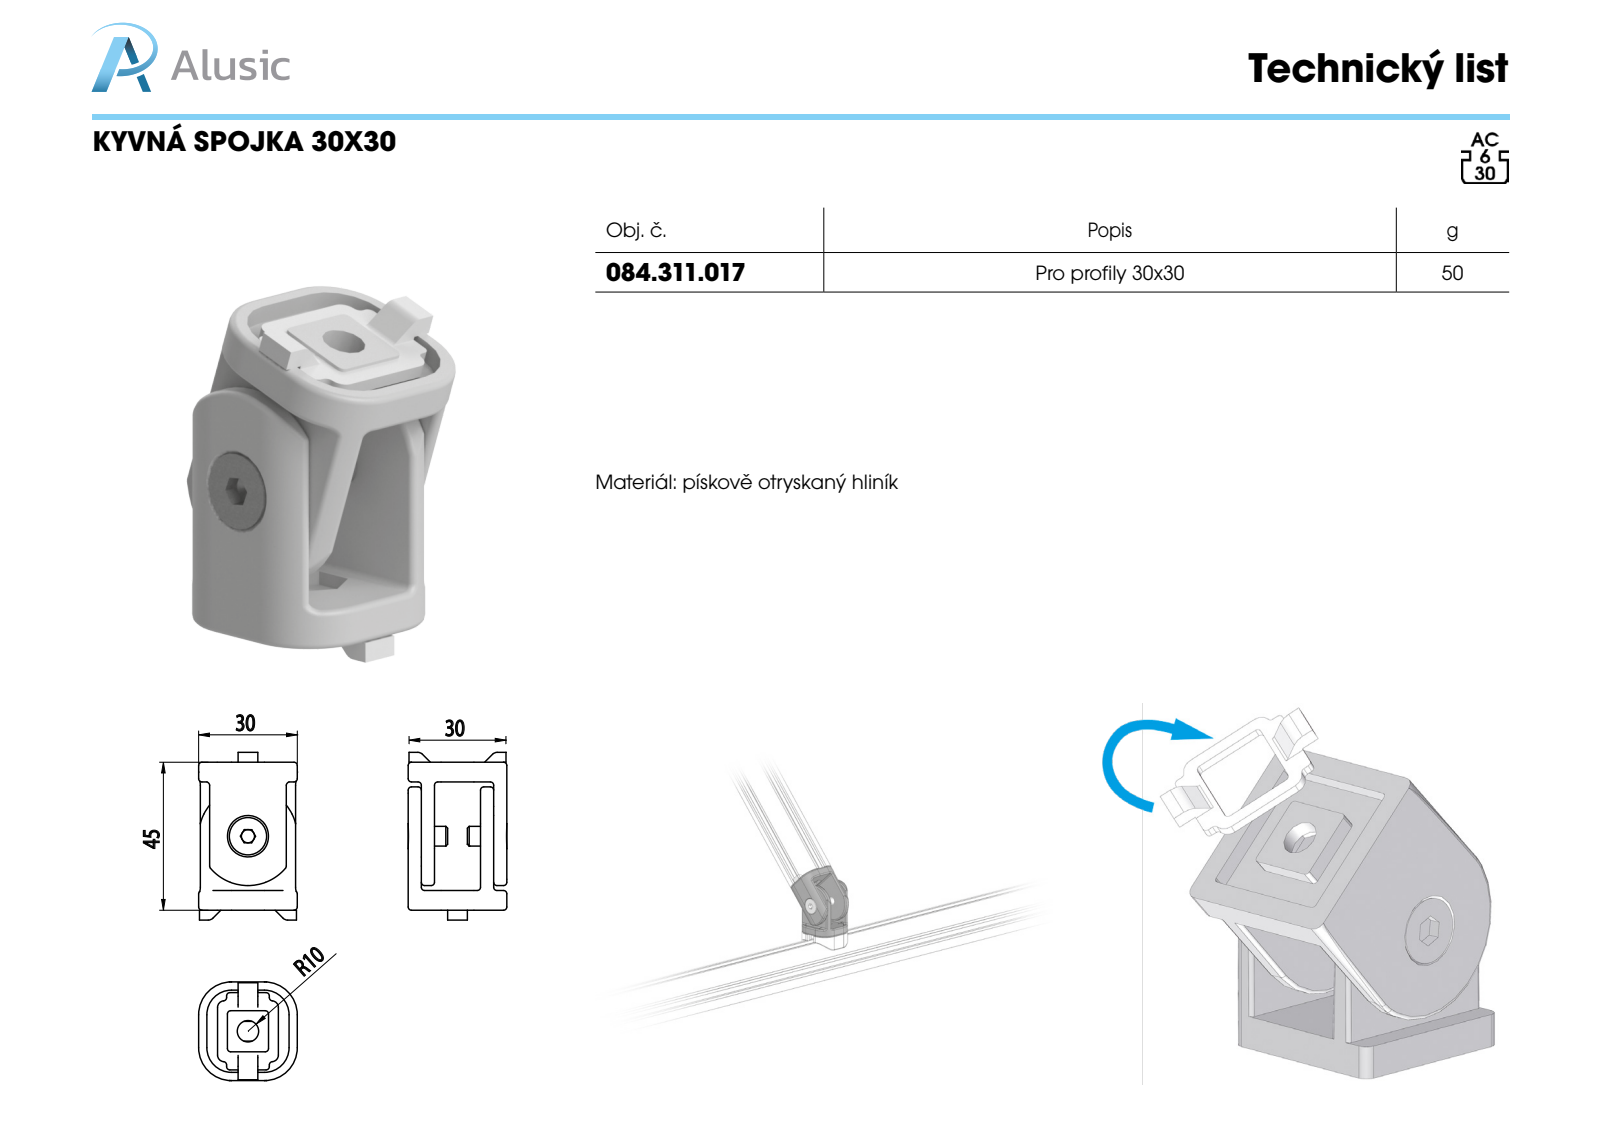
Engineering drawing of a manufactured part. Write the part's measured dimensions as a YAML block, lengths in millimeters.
part_name: "084.311.017; 084.311.009-2; socket countersunk head screw_iso_ISO 10642 - M6 x 12 --- 12N; 084.311.017L"
step_written_by: "SolidWorks 2012 (CONFIG_CONTROL_DESIGN)"
units: millimeters
bodies: {solids: 6, faces: 360, planar: 136, cylindrical: 128, other: 96}
overall_size: [51.93, 44.4, 30]
volume: 19576
surface_area: 14537
round_holes:
  - {diameter: 6.5, count: 2}
  - {diameter: 5, count: 1}
  - {diameter: 6.6, count: 1}
round_bosses_or_shafts:
  - {diameter: 11.34, count: 1}
  - {diameter: 6, count: 1}
partial_cylinders:
  - {radius: 1, count: 60}
  - {radius: 2, count: 12}
  - {radius: 7.5, count: 8}
  - {radius: 10, count: 8}
  - {radius: 15, count: 1}
face_to_face_distances: [4, 22, 18, 3, 2.5, 0.5, 8, 14, 26, 6]
